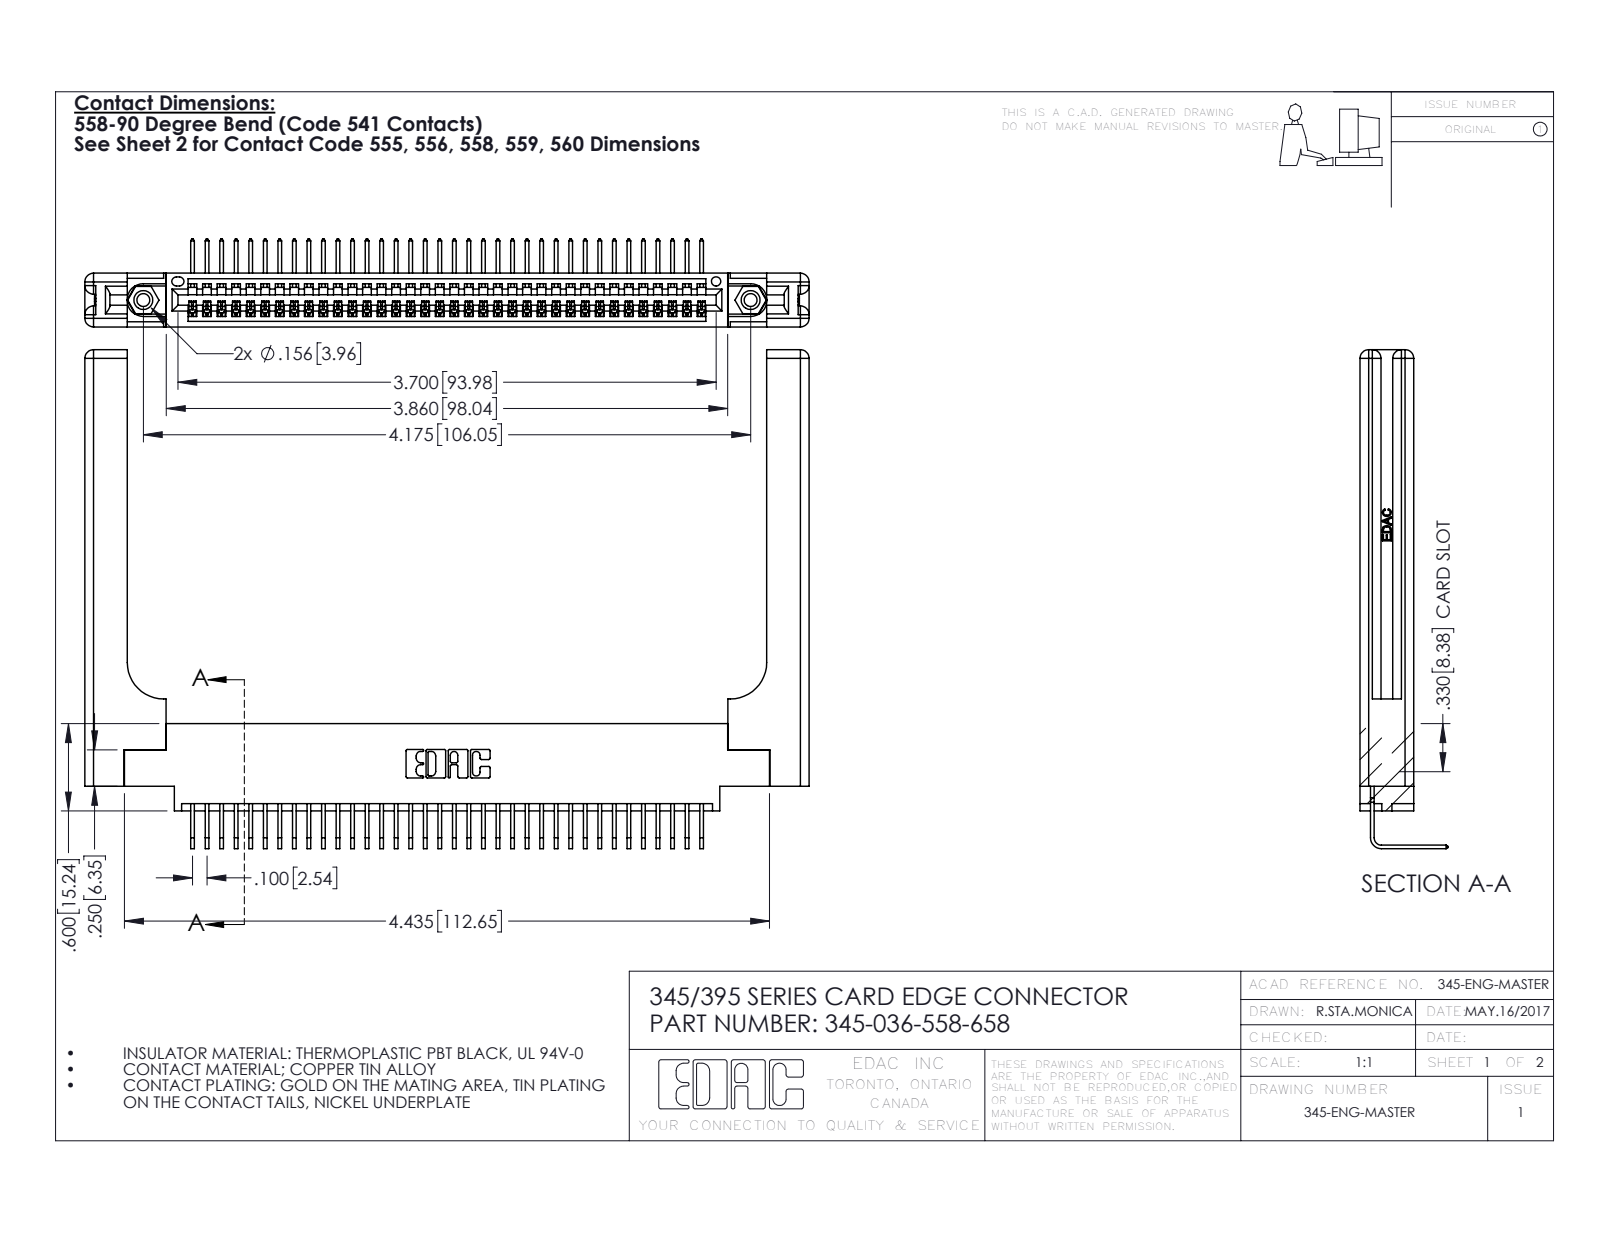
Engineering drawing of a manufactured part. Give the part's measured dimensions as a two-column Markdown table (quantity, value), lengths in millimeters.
| quantity | value |
| --- | --- |
| part name | 345 Part_0.170 Offset - 0.156 Dia-TH; 345-292-001_558 Tail - 2; 345-036-558-658; 345-220-058_345-220-058 (+1 more) |
| STEP written by | SolidWorks 2016 (CONFIG_CONTROL_DESIGN) |
| units | millimeters |
| bodies | 41 solids, 2546 faces (1744 planar, 742 cylindrical, 60 other) |
| overall size | 126.5 × 87.1 × 15.4 |
| volume | 20 470 mm³ |
| surface area | 21 960 mm² |
| round holes (diameter × count) | 2.3 × 2, 3.2 × 2, 4 × 2, 1.6 × 1 |
| round bosses / shafts (diameter × count) | 3.9 × 2 |
| partial cylindrical surfaces (radius × count) | 0.2 × 72, 0.3 × 22, 1.5 × 16, 0.2 × 6, 0.8 × 6, 0.7 × 3, 0.8 × 2, 0.8 × 2 |
| main face-to-face distances | 9.4, 1.8, 7.6, 2.5, 6.9, 0.6, 5.1, 3.8, 3.8, 5.7 |
| hole center spacings | 6.9, 100.1, 106 |
